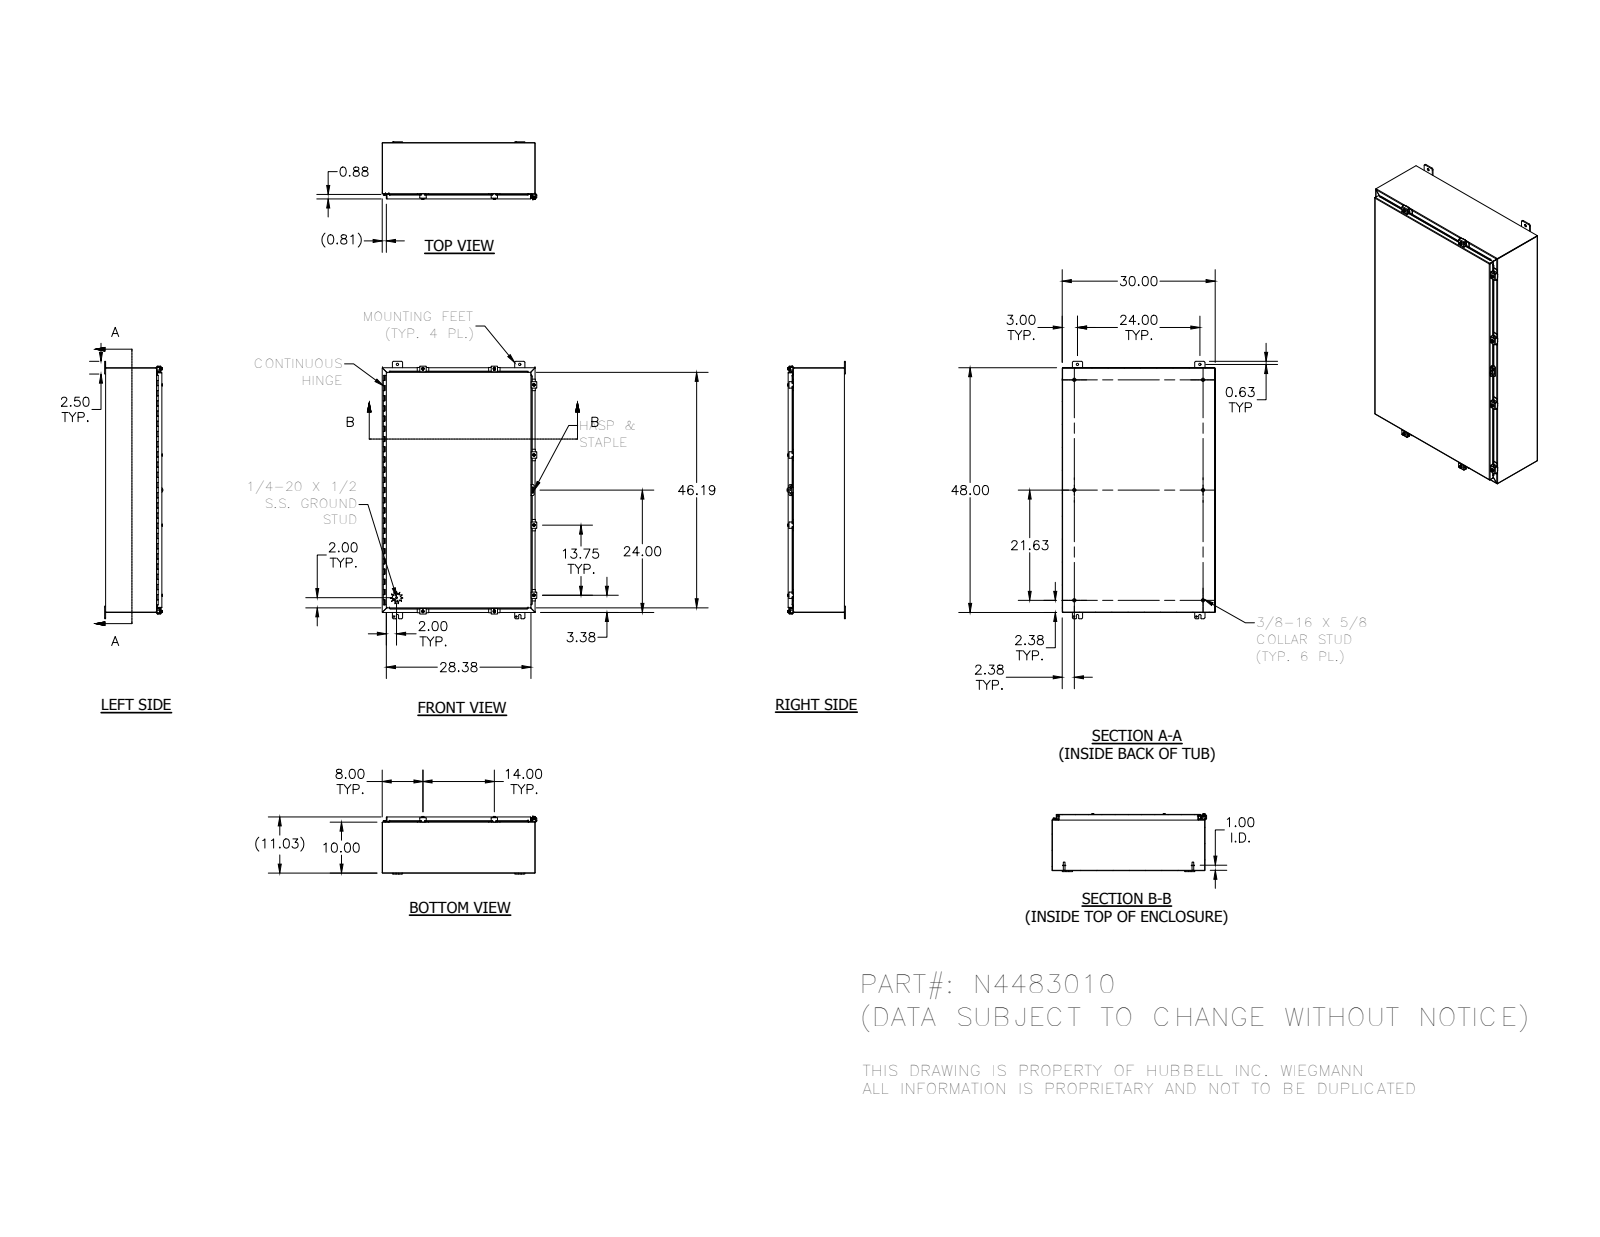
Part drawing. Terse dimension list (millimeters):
name: 328115T_1; N43010TB_1; N4483010; HFW30825-2_1 (+8 more)
written by: SolidWorks 2014 (AUTOMOTIVE_DESIGN)
unit: mm
bodies: 61 solids, 2368 faces (983 planar, 1032 cylindrical, 353 other)
size: 1282.7 × 769.9 × 289.8
volume: 6 278 000 mm³; area: 6 534 000 mm²
holes: 8× ⌀5.4, 8× ⌀7.1, 8× ⌀7.6, 4× ⌀8, 4× ⌀11.1, 3× ⌀2.8, 1× ⌀3.2, 1× ⌀4, 1× ⌀12.7
bosses: 10× ⌀6.4, 8× ⌀13.2, 8× ⌀12.7, 8× ⌀8.9, 6× ⌀15.9, 6× ⌀8.4, 1× ⌀8.6, 1× ⌀3
rounds: 95× R0.8, 39× R3.2, 35× R6.4, 21× R0.8, 21× R2.7, 20× R1.6, 16× R3.6, 12× R2.5
face distances: 1.9, 278.4, 276.5, 280.2, 760.1, 1217.3, 758.2, 762, 252.1, 26.2
hole spacings: 40.5, 609.6, 1219.2, 1363.1, 349.3, 20.1, 127.5, 128.7
